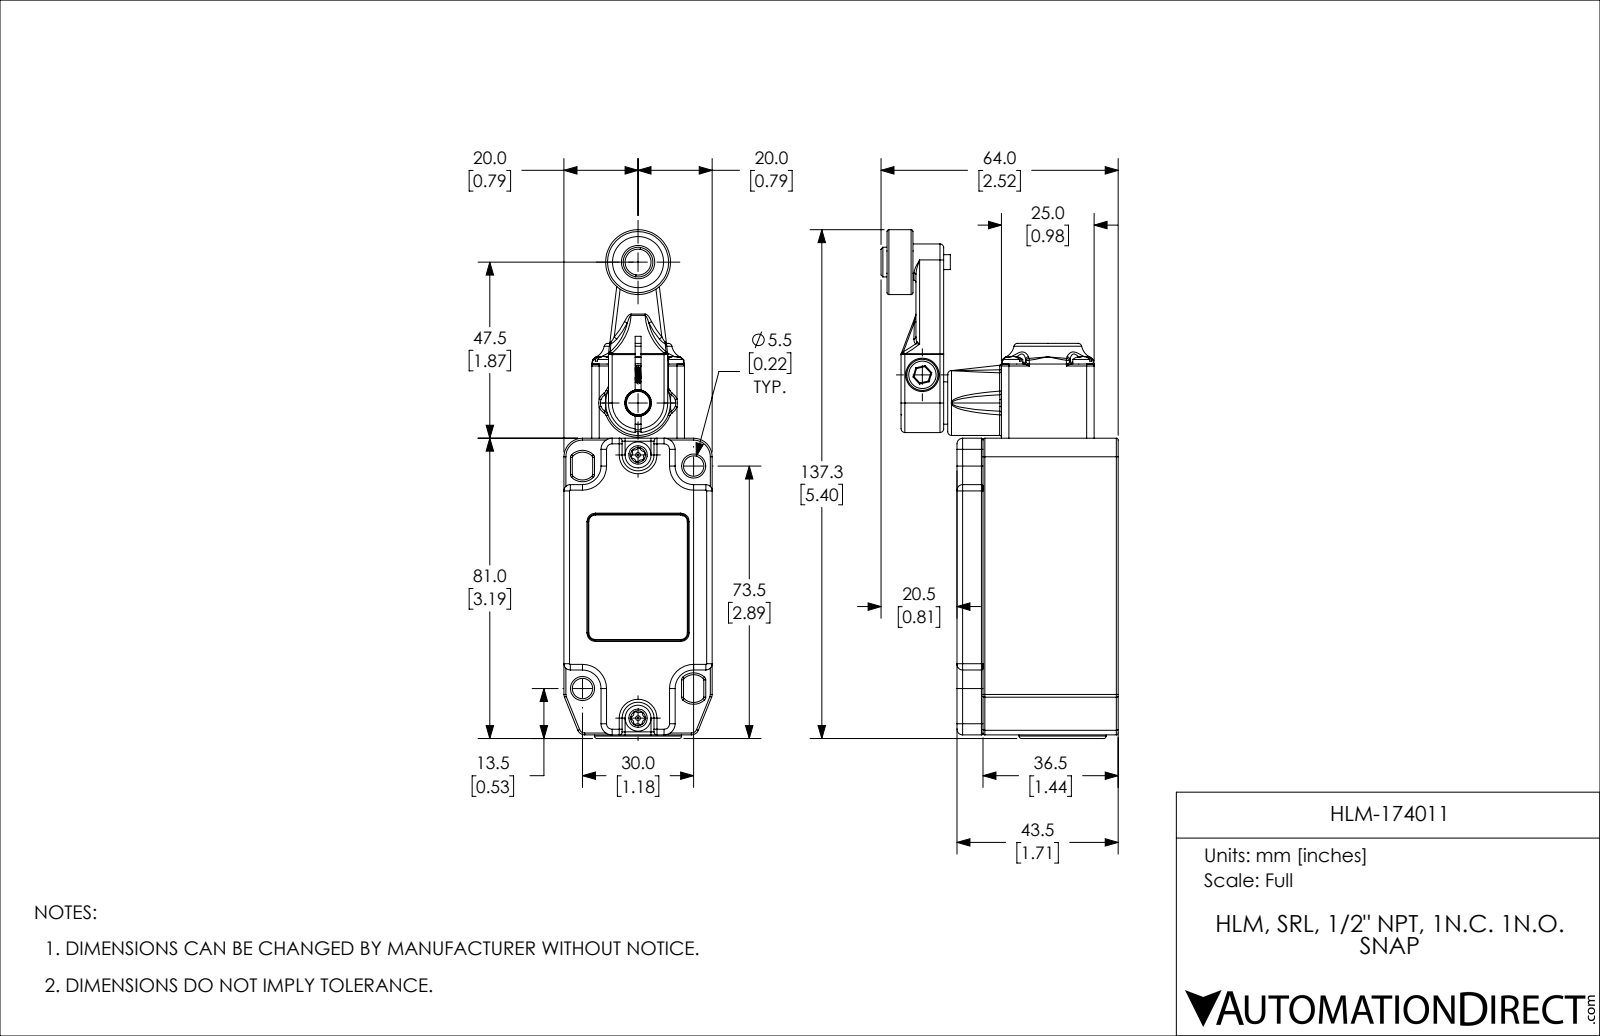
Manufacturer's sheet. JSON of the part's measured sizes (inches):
{"part_name": "174-HLM (short Roller lever) (step format)", "step_written_by": "SolidWorks 2013 (CONFIG_CONTROL_DESIGN)", "units": "inches", "bodies": {"solids": 17, "faces": 2938, "planar": 676, "cylindrical": 681, "other": 1581}, "overall_size": [5.404, 2.52, 1.575], "volume_in3": 4.498, "surface_area_in2": 83.05, "round_holes": [[0.118, 10], [0.106, 4], [0.134, 4], [0.146, 2], [0.15, 2], [0.157, 2], [0.165, 2], [0.217, 2], [0.571, 2], [0.138, 1], [0.161, 1], [0.173, 1]], "round_bosses_or_shafts": [[0.244, 6], [0.216, 4], [0.689, 2], [0.276, 2], [0.252, 2], [0.051, 2], [0.925, 1], [0.728, 1]], "partial_cylinders_radius": [[0.02, 168], [0.039, 44], [0.016, 26], [0.006, 14], [0.012, 12], [0.079, 12], [0.031, 10], [0.059, 9]], "face_to_face_distances": [0.089, 1.486, 1.575, 0.098, 1.398, 1.512, 0.102, 1.61, 0.173, 1.713], "hole_center_spacings": [0.748, 0.529, 1.258, 0.354, 0.432, 0.65, 0.75, 0.828]}
